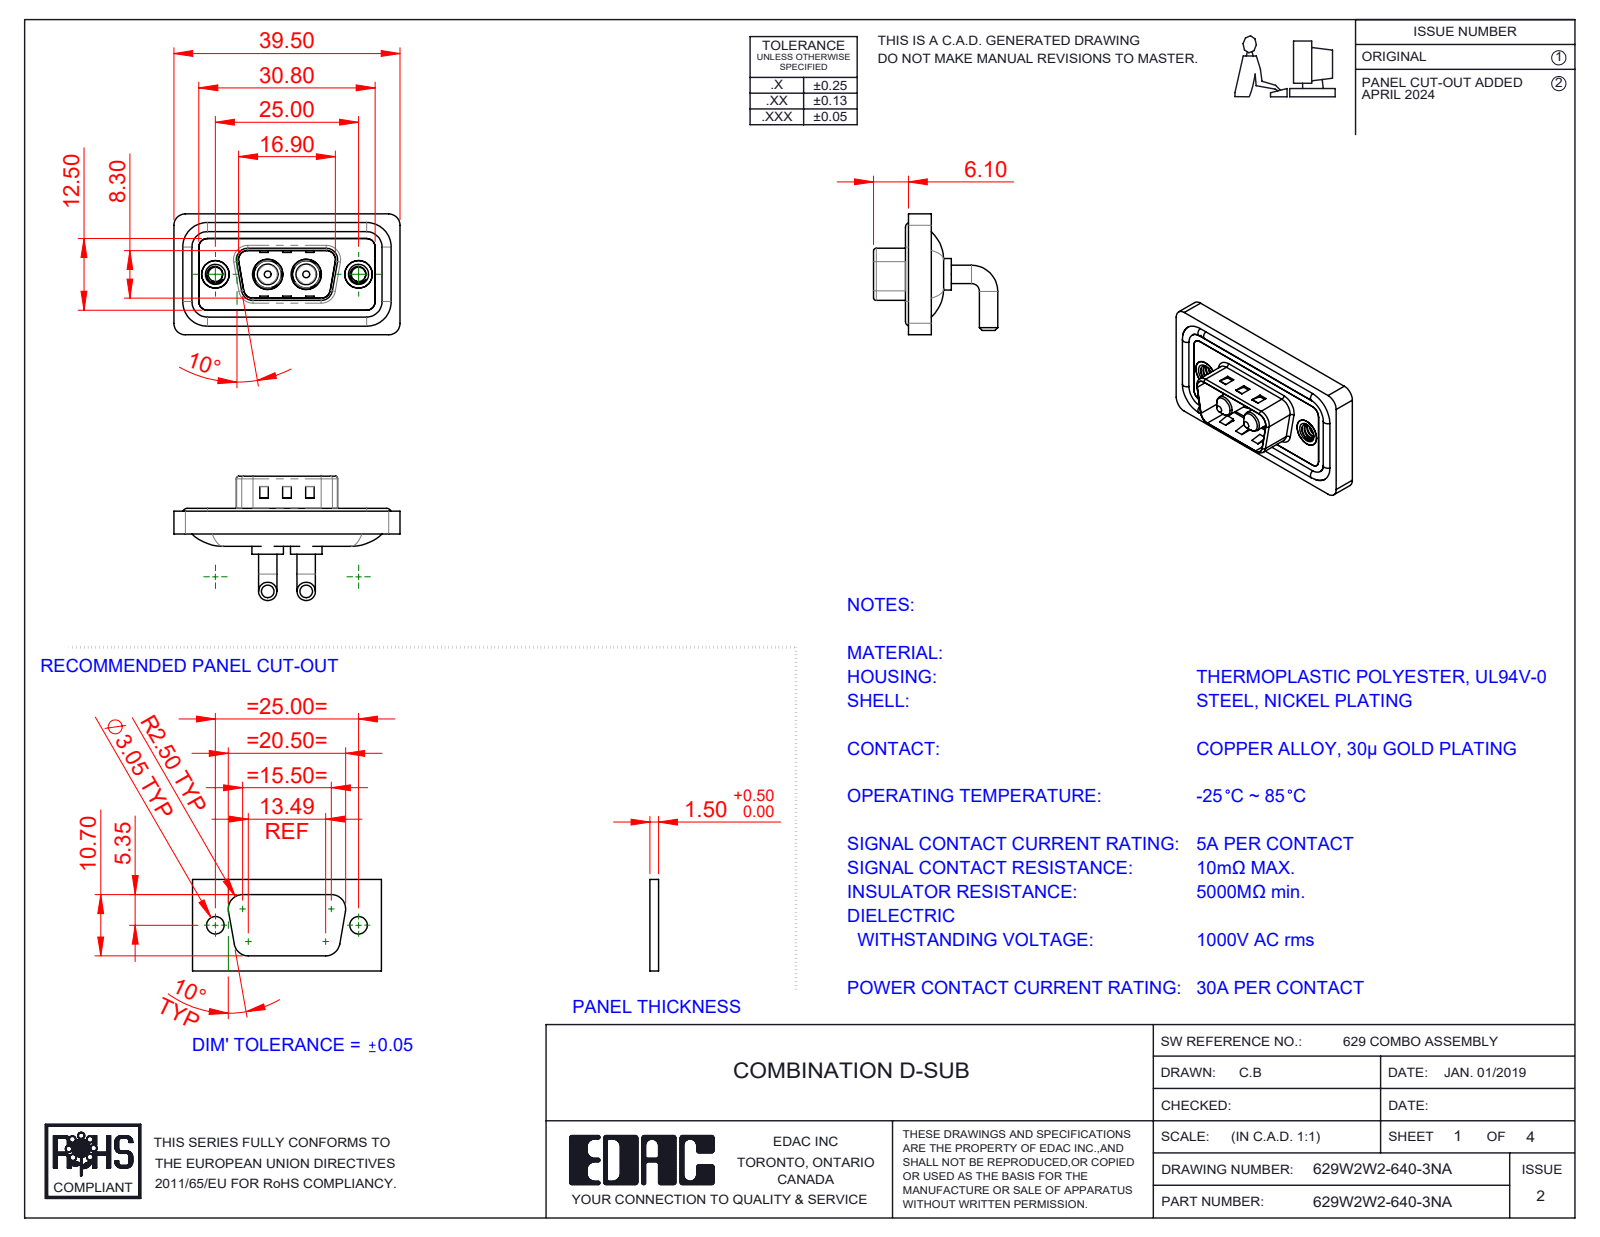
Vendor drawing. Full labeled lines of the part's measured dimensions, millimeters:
Part name (STEP PRODUCT): Power Pin_30A RA; 629W2W2-640-3NA; 629Combo Shell Front_09 Contacts; 629Combo Waterproof Housing_09 Contacts (+3 more)
STEP written by: SolidWorks 2023 (CONFIG_CONTROL_DESIGN)
Units: millimetres
Bodies: 11 solids, 491 faces (165 planar, 220 cylindrical, 106 other)
Overall size (bounding box): 39.5 × 21.7 × 21.1
Volume: 4 644 mm³ · Surface area: 7 208 mm²
Round holes (diameter × count): ⌀2.5 ×2, ⌀4 ×2, ⌀4.8 ×2, ⌀4.85 ×2, ⌀5 ×2, ⌀5.3 ×2
Round bosses / shafts (diameter × count): ⌀3.2 ×4, ⌀1.6 ×4, ⌀5.5 ×2, ⌀5.2 ×2, ⌀4.9 ×2, ⌀4.75 ×2, ⌀3.75 ×2, ⌀3.6 ×2
Partial cylindrical surfaces — rounded edges, fillets, slot ends (radius × count): R1.5 ×18, R2 ×18, R0.5 ×8, R1.6 ×8, R0.25 ×4, R0.6 ×4, R0.65 ×4, R0.9 ×4
Main face-to-face distances: 0.4, 2.9, 1.1, 0.8, 2.1, 2.5, 3.1, 1.6, 4.5, 1.5
Hole centre spacings: 9.14, 15.86, 6.72, 25
